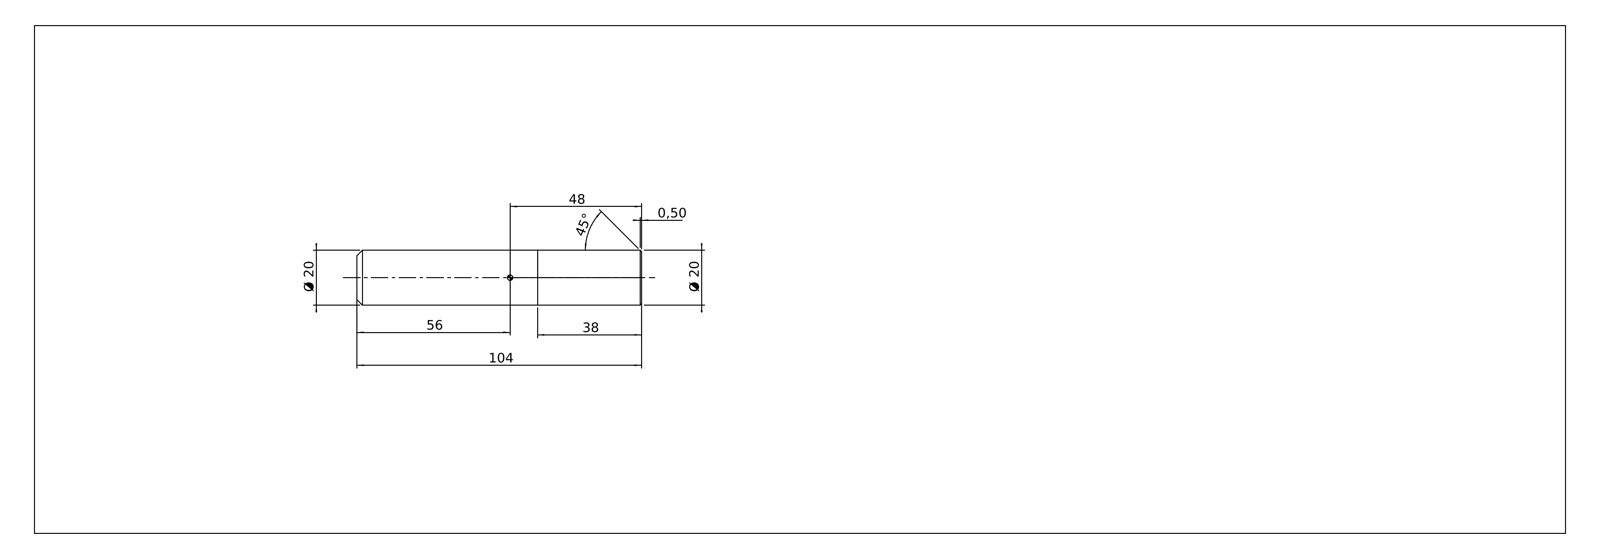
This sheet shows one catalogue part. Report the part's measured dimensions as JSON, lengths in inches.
{"part_name": "735.200.00", "step_written_by": "SolidWorks 2019 (CONFIG_CONTROL_DESIGN)", "units": "inches", "bodies": {"solids": 2, "faces": 8, "planar": 4, "cylindrical": 2, "other": 2}, "overall_size": [4.094, 0.787, 0.787], "volume_in3": 1.986, "surface_area_in2": 11.93, "round_bosses_or_shafts": [[0.787, 1]], "face_to_face_distances": [1.496, 4.094, 2.598]}
